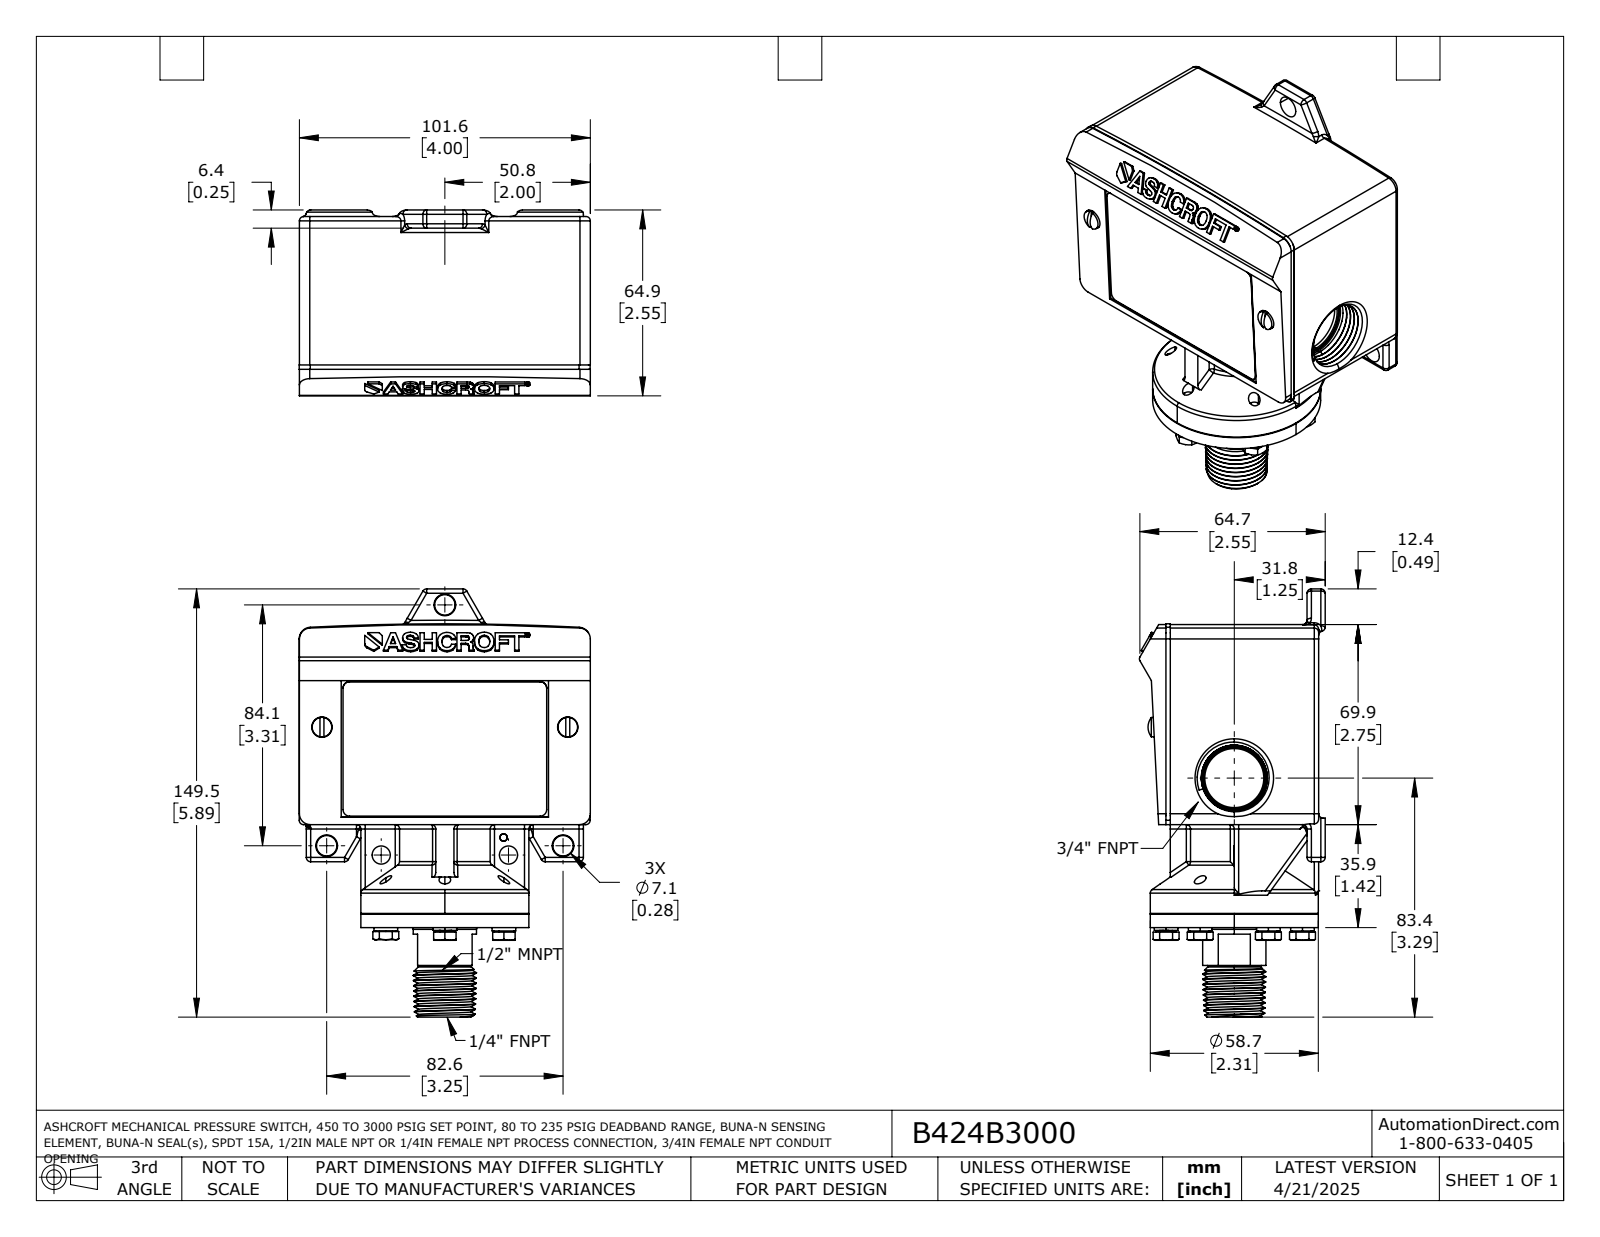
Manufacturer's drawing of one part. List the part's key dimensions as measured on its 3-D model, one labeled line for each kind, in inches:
Part name (STEP PRODUCT): B424B3000
STEP written by: SolidWorks 2021 (AUTOMOTIVE_DESIGN)
Units: inches
Bodies: 1 solid, 1203 faces (301 planar, 478 cylindrical, 424 other)
Overall size (bounding box): 5.885 × 4.003 × 2.555
Volume: 29.06 in³ · Surface area: 89.18 in²
Round holes (diameter × count): ⌀0.161 ×6, ⌀0.187 ×5, ⌀0.192 ×5, ⌀0.209 ×5, ⌀0.28 ×2, ⌀0.812 ×1
Round bosses / shafts (diameter × count): ⌀0.325 ×6, ⌀0.278 ×6, ⌀0.19 ×5, ⌀0.27 ×2, ⌀0.25 ×2, ⌀2.31 ×1, ⌀0.87 ×1
Partial cylindrical surfaces — rounded edges, fillets, slot ends (radius × count): R0.06 ×92, R0.09 ×4, R0.15 ×4, R0.16 ×2, R0.625 ×2, R36 ×2, R0.03 ×1, R0.05 ×1
Main face-to-face distances: 4, 1.415, 0.015, 0.09, 3.91, 0.44, 3.56, 3.47, 0.35, 0.845
Hole centre spacings: 1.624, 0.937, 1.875, 0.938, 3.38
